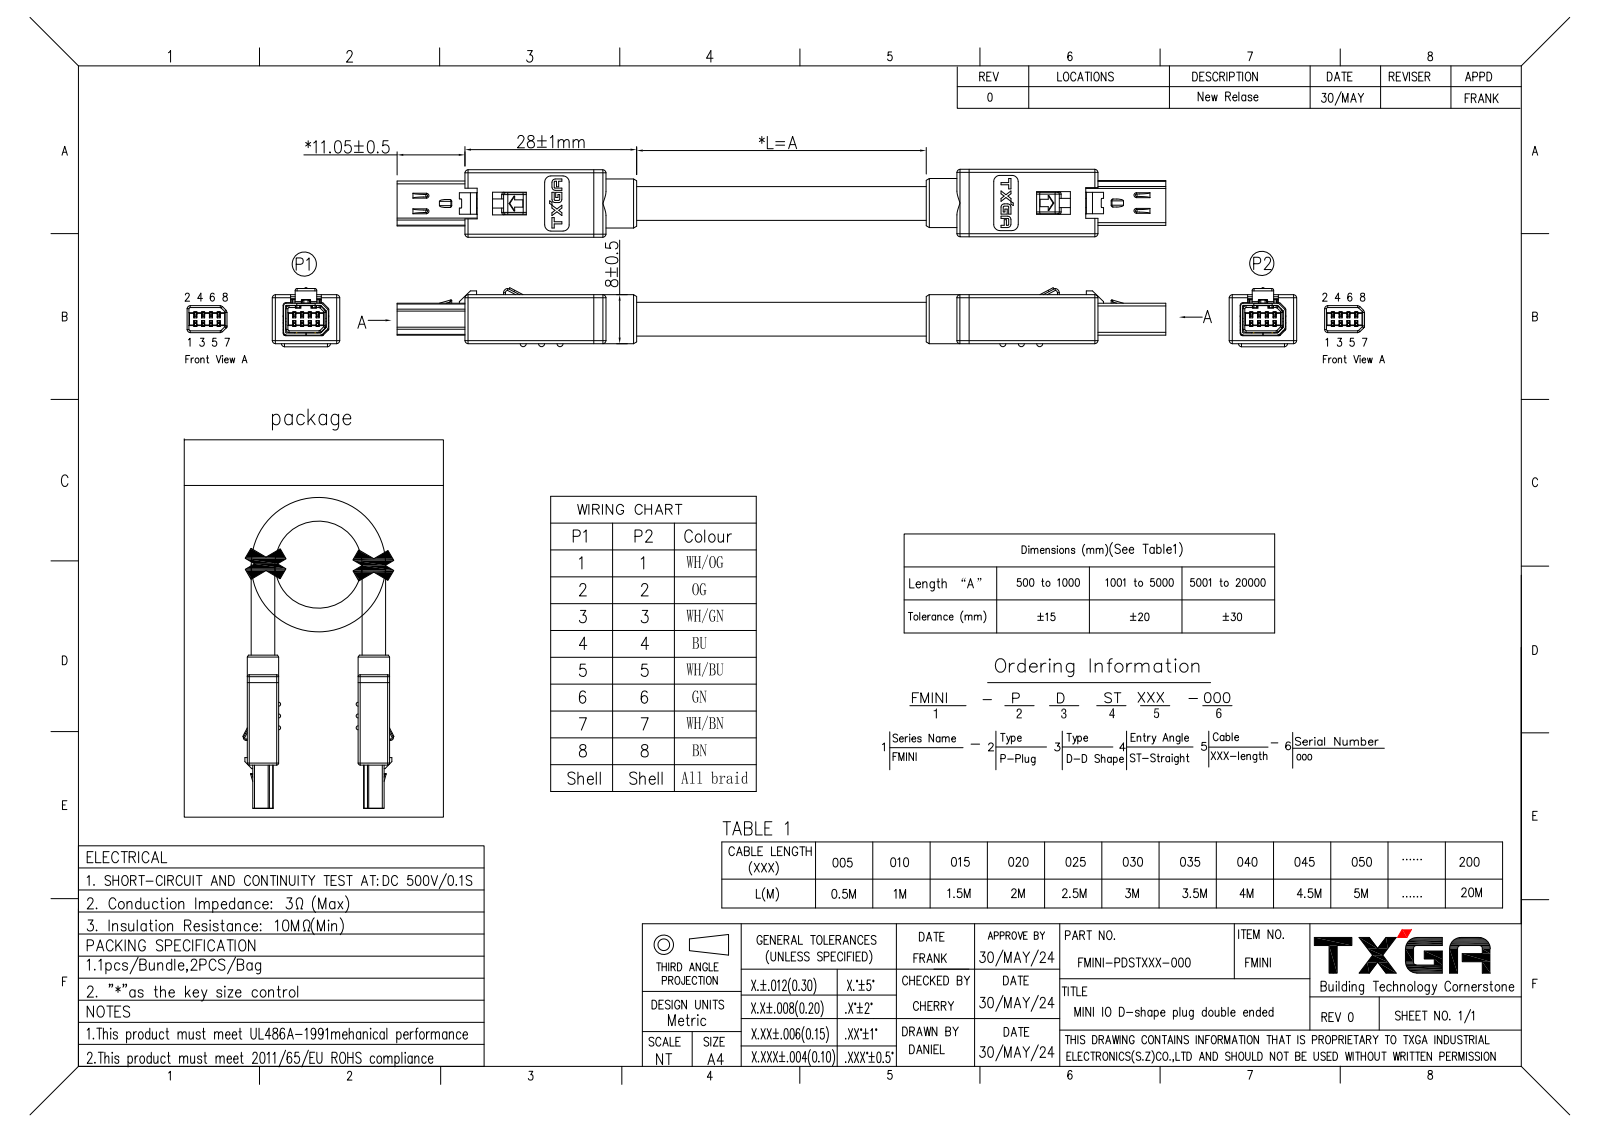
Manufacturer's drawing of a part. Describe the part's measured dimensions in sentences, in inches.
The part is named "PRT0001". Its 3-D file was written by "PRO/ENGINEER BY PARAMETRIC TECHNOLOGY CORPORATION, 2010280 (CONFIG_CONTROL_DESIGN)". It is 1 solid with 4582 faces: 3058 planar, 1136 cylindrical and 388 other. Overall it measures 4.335 by 0.433 by 0.379 inches. Its volume is 0.276 cubic inches and its surface area 14.35 square inches. Round bosses or shafts: 1 of diameter 0.315, 1 of diameter 0.197. Partial cylindrical surfaces (rounded edges, fillets, slot ends): 110 of radius 0.008, 76 of radius 0.004, 68 of radius 0.012, 60 of radius 0.02, 40 of radius 0.031, 38 of radius 0.018, 20 of radius 0.016, 16 of radius 0.039. The main face-to-face distances are 0.014, 0.026, 0.055, 0.03, 0.069, 0.191, 0.039, 0.02, 0.246, 0.26.
